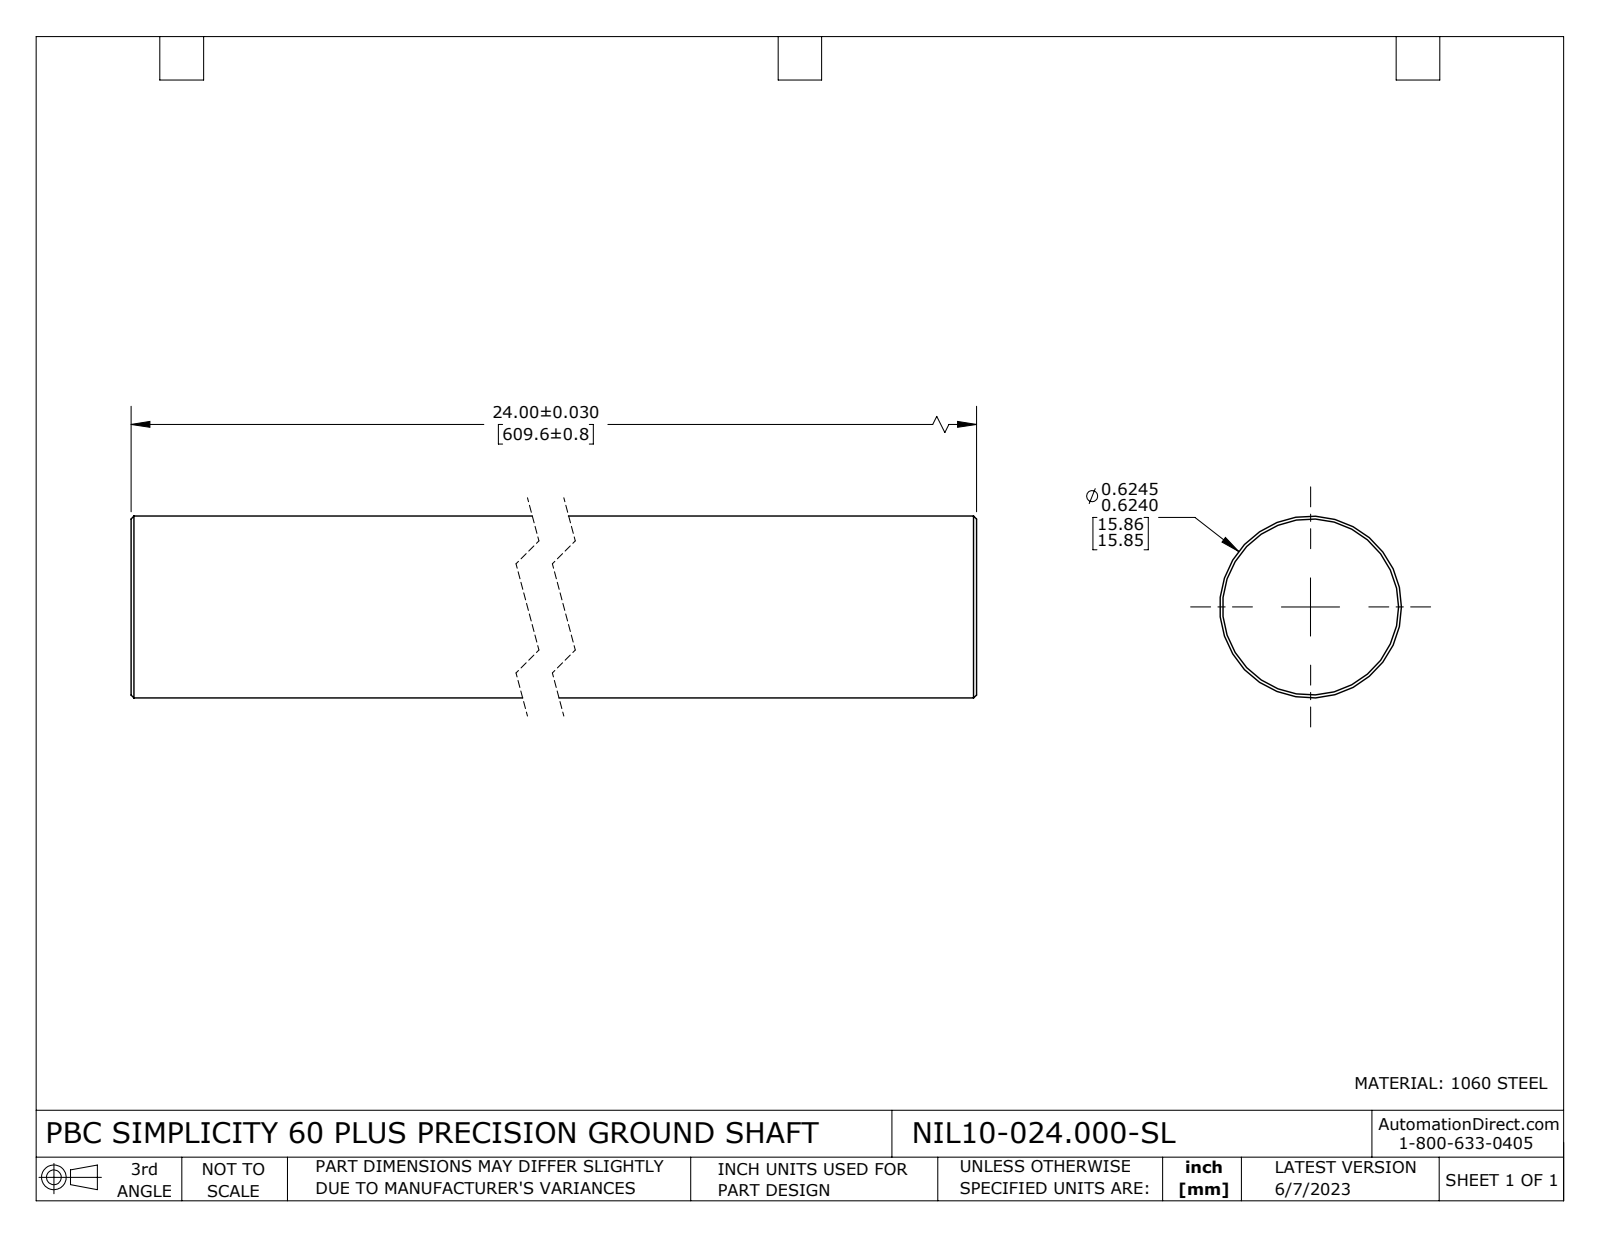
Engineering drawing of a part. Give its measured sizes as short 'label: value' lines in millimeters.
name: NIL10-024.000-SL
written by: SolidWorks 2021 (CONFIG_CONTROL_DESIGN)
unit: mm
bodies: 1 solid, 8 faces (2 planar, 2 cylindrical, 4 other)
size: 609.6 × 15.9 × 15.9
volume: 120 700 mm³; area: 30 780 mm²
bosses: 1× ⌀15.9
face distances: 609.6
